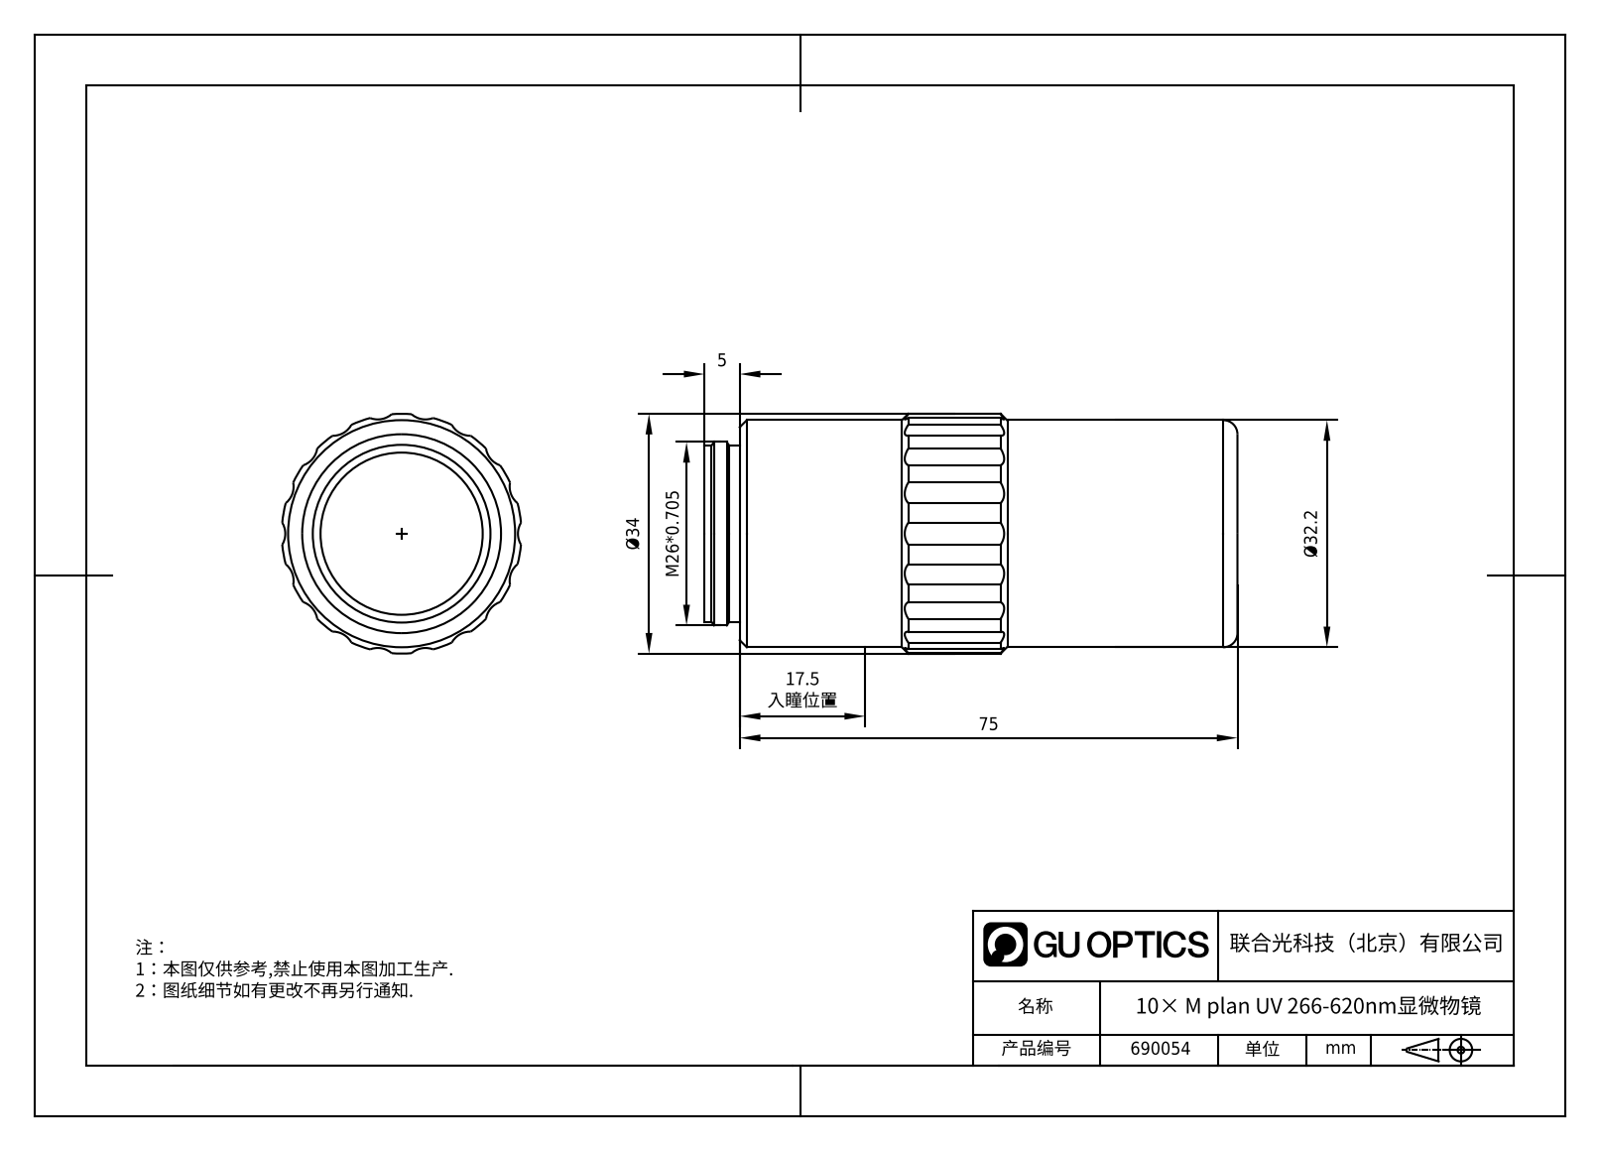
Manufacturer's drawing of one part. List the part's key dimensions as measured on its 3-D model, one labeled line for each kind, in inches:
Part name (STEP PRODUCT): 690054
STEP written by: SolidWorks 2020 (CONFIG_CONTROL_DESIGN)
Units: inches
Bodies: 1 solid, 55 faces (6 planar, 43 cylindrical, 6 other)
Overall size (bounding box): 3.15 × 1.339 × 1.333
Volume: 3.921 in³ · Surface area: 15.17 in²
Round holes (diameter × count): ⌀0.472 ×1, ⌀0.591 ×1
Round bosses / shafts (diameter × count): ⌀1.268 ×1, ⌀1.024 ×1, ⌀0.984 ×1
Partial cylindrical surfaces — rounded edges, fillets, slot ends (radius × count): R0.118 ×18, R0.669 ×1
Main face-to-face distances: 3.15, 0.039, 3.11, 0.197, 2.953, 2.913, 0.157, 3.071, 1.693, 1.654
